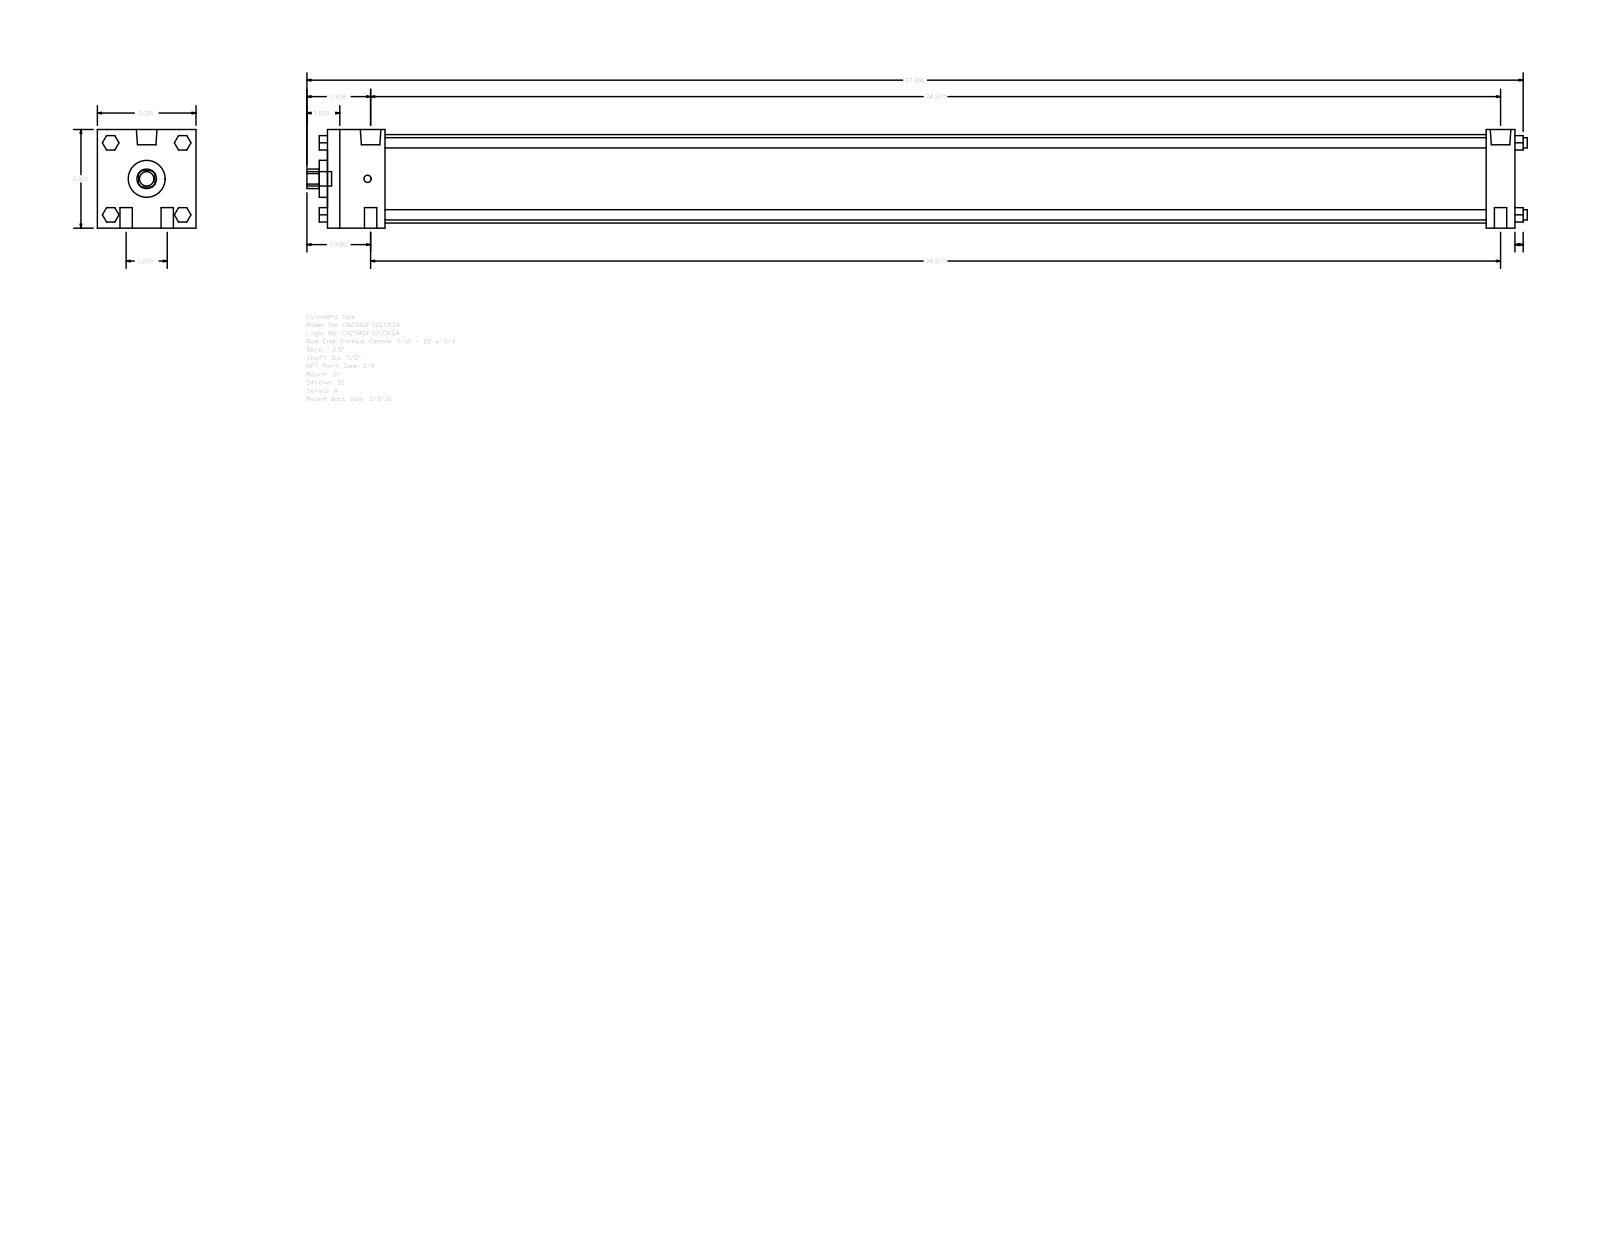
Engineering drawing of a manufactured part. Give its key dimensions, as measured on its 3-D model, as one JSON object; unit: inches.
{"part_name": "A_SF__0250_0.625", "step_written_by": "GSSL Pune (CONFIG_CONTROL_DESIGN)", "units": "inches", "bodies": {"solids": 0, "faces": 124, "planar": 94, "cylindrical": 30, "other": 0}, "overall_size": [37.125, 3, 3], "round_holes": [[0.625, 1], [1.125, 1], [2.69, 1]], "round_bosses_or_shafts": [[0.375, 4], [0.313, 4], [0.627, 2], [0.219, 2], [0.437, 1]], "partial_cylinders_radius": [[0.297, 1]], "face_to_face_distances": [3, 36.125, 1.75, 35.25, 0.875, 33.5, 34.375, 0.25, 36.375, 2]}
